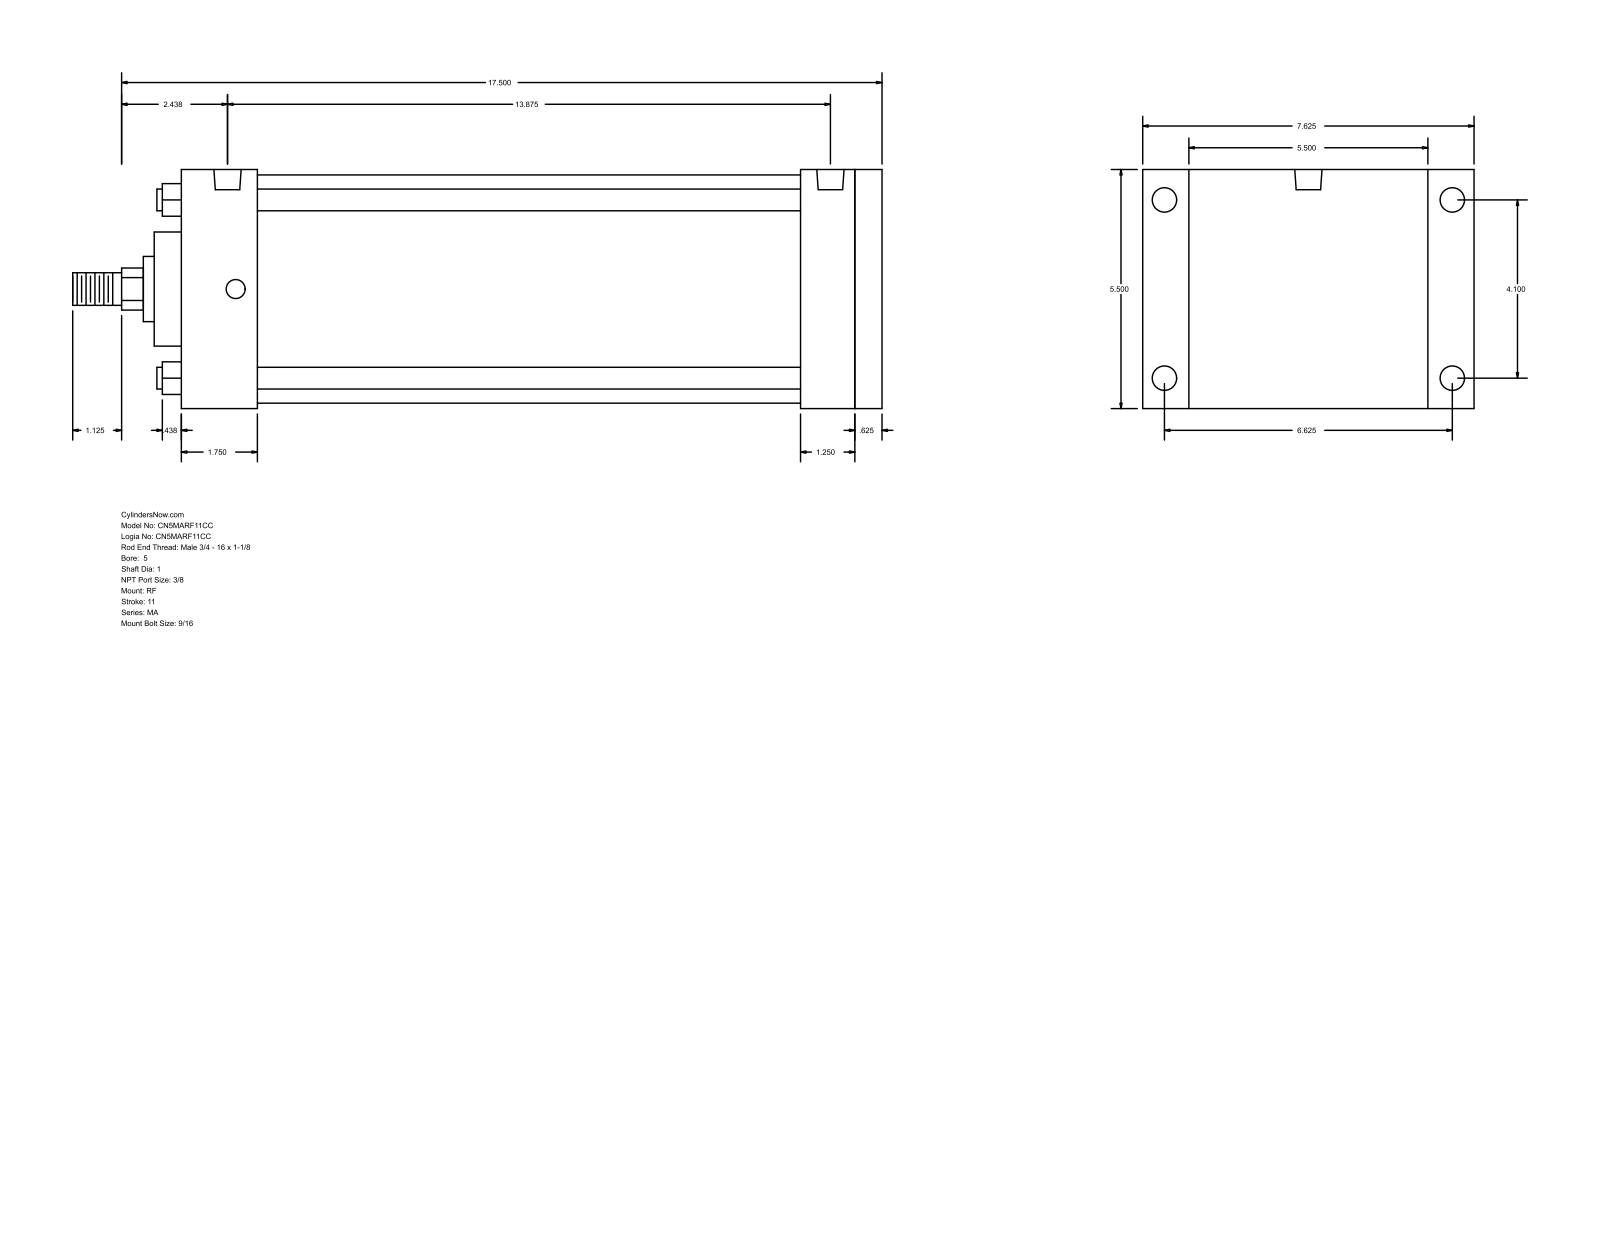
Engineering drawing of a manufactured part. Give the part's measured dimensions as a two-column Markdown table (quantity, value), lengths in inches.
| quantity | value |
| --- | --- |
| part name | MA_RF__0500_1 |
| STEP written by | GSSL Pune (CONFIG_CONTROL_DESIGN) |
| units | inches |
| bodies | 0 solids, 94 faces (65 planar, 29 cylindrical, 0 other) |
| overall size | 18.625 × 7.625 × 5.5 |
| round holes (diameter × count) | 0.437 × 4, 0.563 × 4, 0.627 × 2 |
| round bosses / shafts (diameter × count) | 0.5 × 4, 5.25 × 1, 2.625 × 1, 1.5 × 1, 1 × 1, 0.75 × 1 |
| partial cylindrical surfaces (radius × count) | 0.484 × 1 |
| main face-to-face distances | 5.5, 16.125, 15.5, 0.625, 1.875, 1.75, 13.75, 14.375, 14.25, 12.5 |
| hole center spacings | 4.1, 6.625, 7.791, 13.5, 0.187, 0.188, 13.687, 13.688 |
